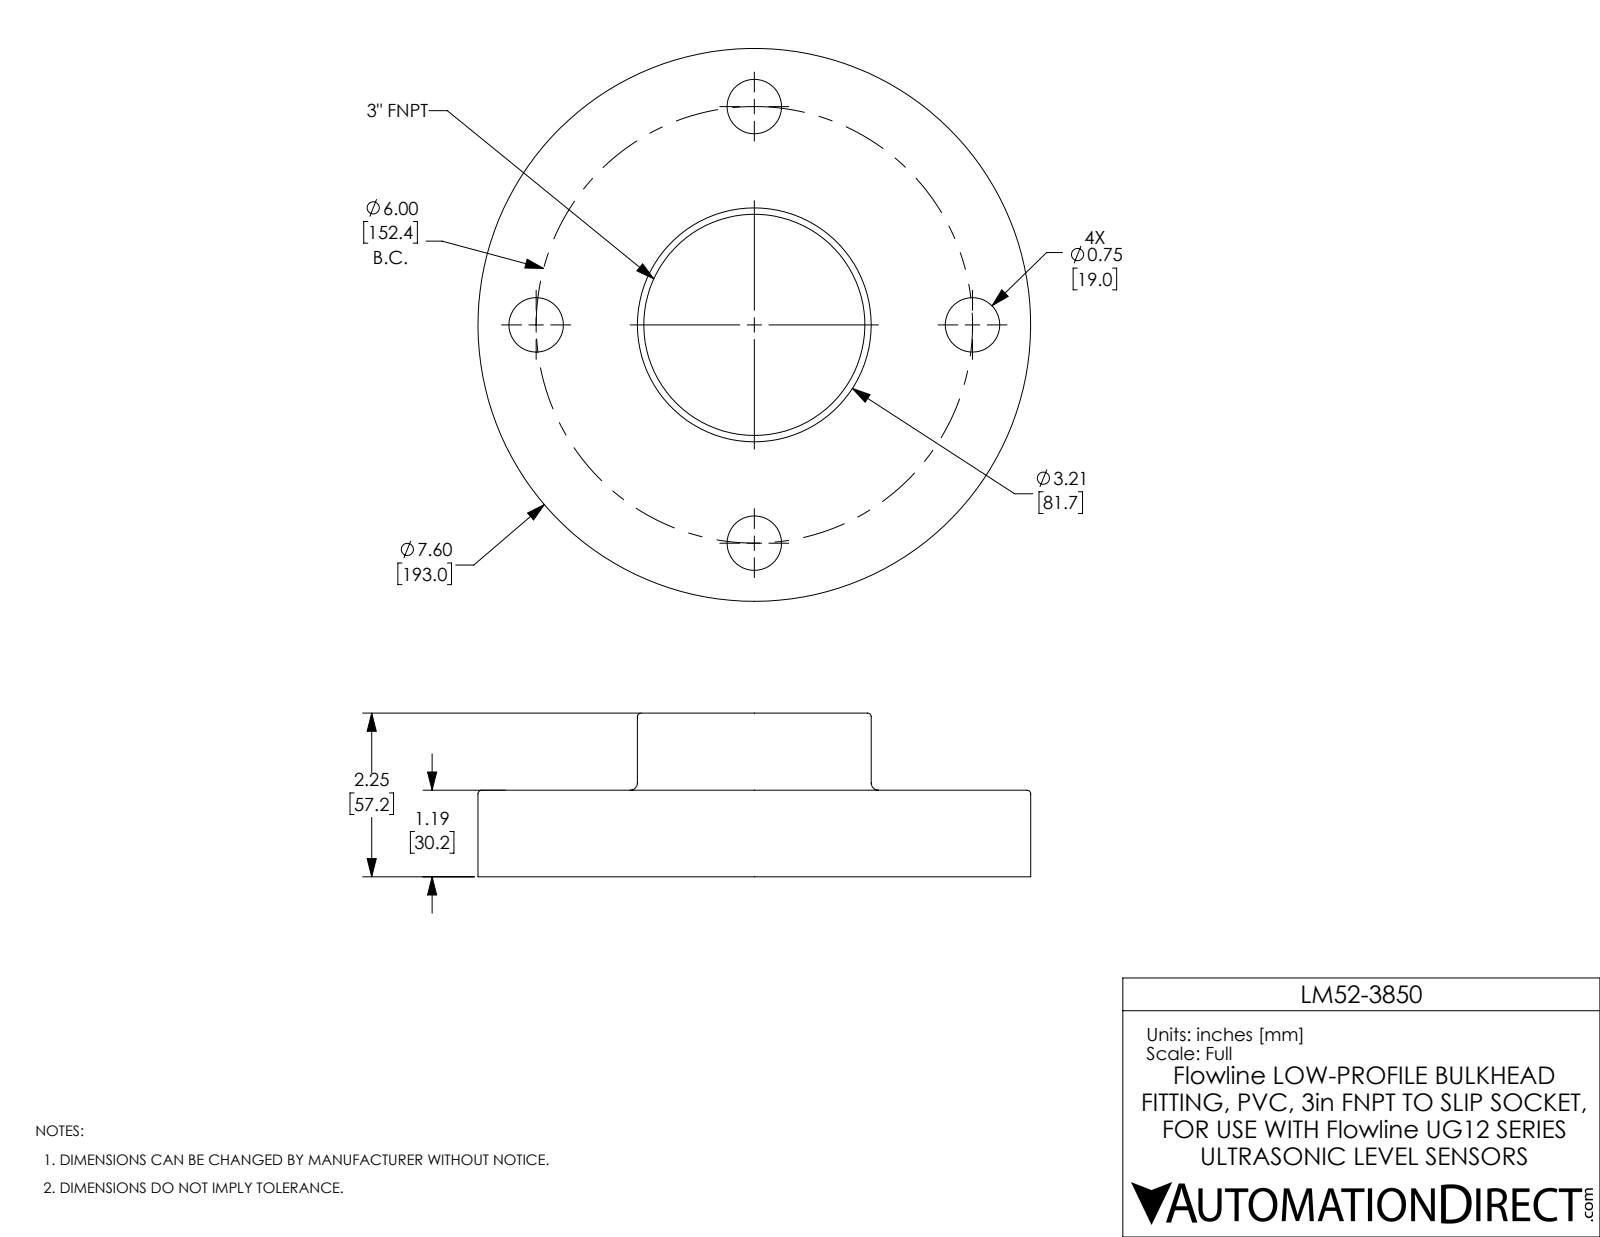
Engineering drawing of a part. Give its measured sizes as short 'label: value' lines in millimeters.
name: LM52-3850
written by: SolidWorks 2017 (AUTOMOTIVE_DESIGN)
unit: mm
bodies: 1 solid, 23 faces (3 planar, 14 cylindrical, 6 other)
size: 193 × 193 × 57.2
volume: 723 700 mm³; area: 92 450 mm²
holes: 4× ⌀19, 1× ⌀77.2
bosses: 1× ⌀193, 1× ⌀81.7
face distances: 30.2, 57.2, 26.9
hole spacings: 76.2, 107.8, 152.4
